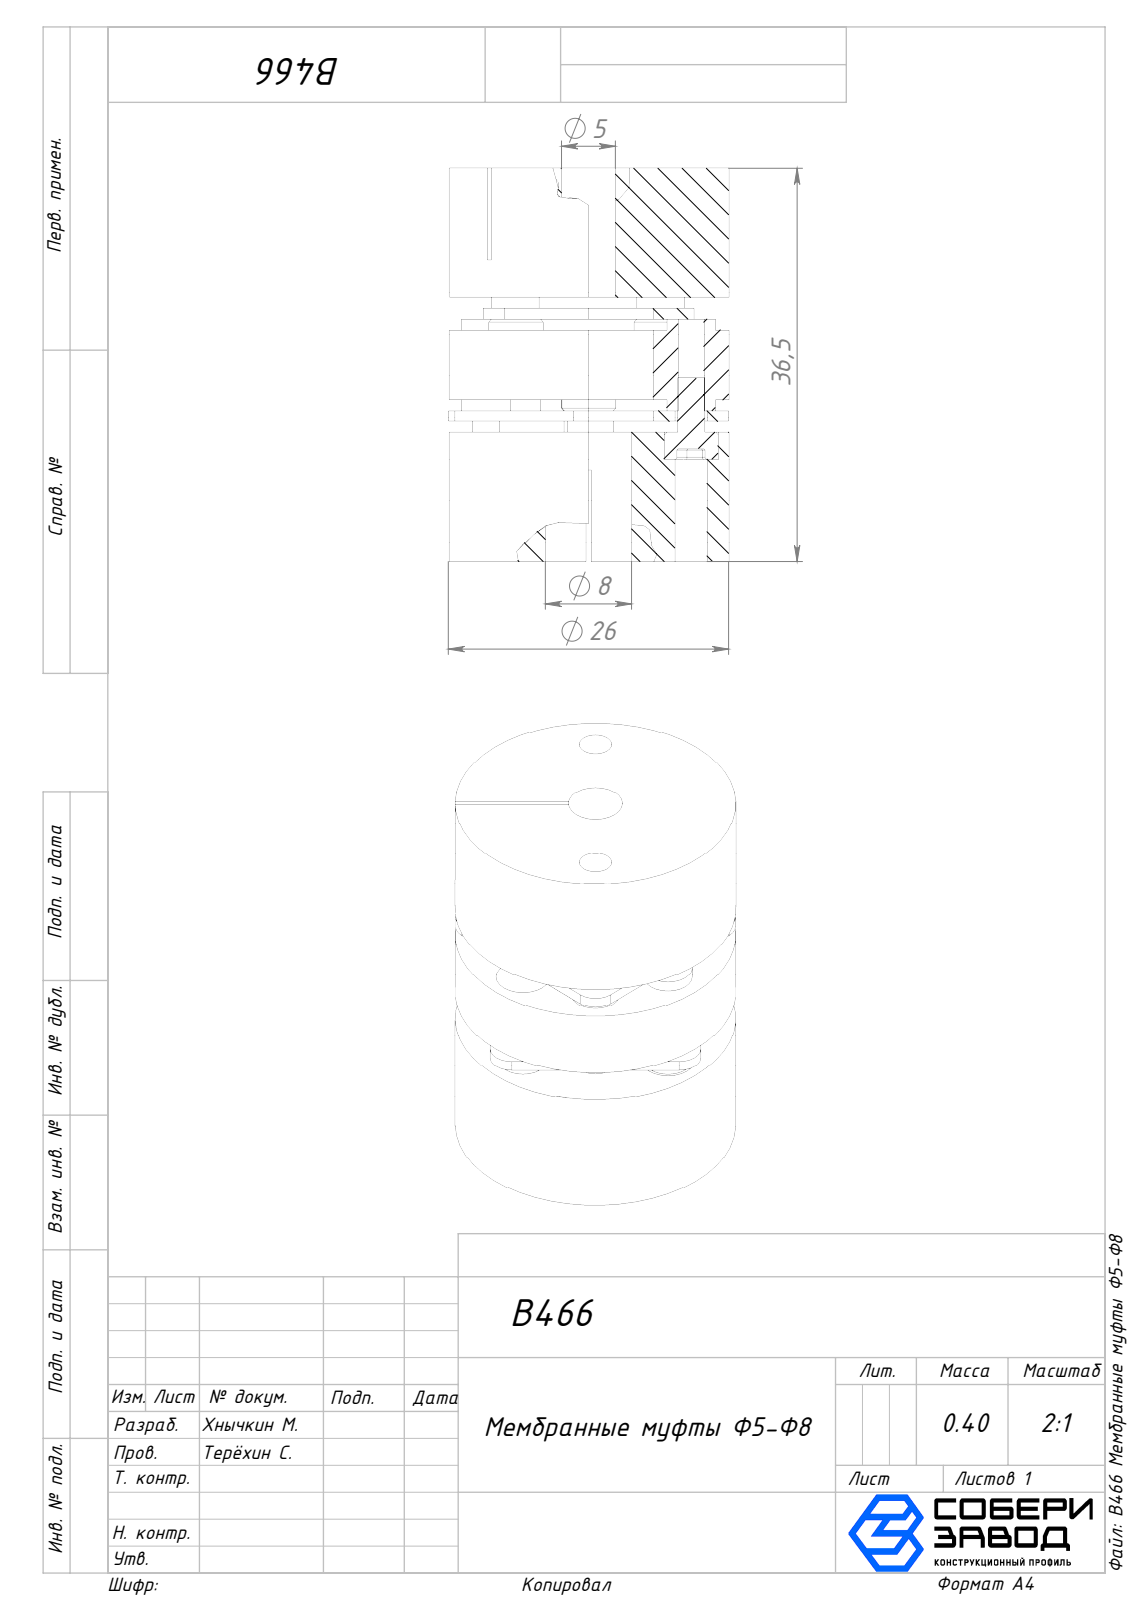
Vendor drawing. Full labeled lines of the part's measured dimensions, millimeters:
Part name (STEP PRODUCT): Средняя часть_00; Верх_00; Винт_00; Ниж.часть_00 (+1 more)
STEP written by: SolidWorks 2025 (AUTOMOTIVE_DESIGN)
Units: millimetres
Bodies: 11 solids, 362 faces (120 planar, 226 cylindrical, 16 other)
Overall size (bounding box): 36.5 × 26 × 26
Volume: 14 511 mm³ · Surface area: 9 746 mm²
Round holes (diameter × count): ⌀5 ×9, ⌀3 ×8, ⌀2.4 ×4, ⌀8 ×1, ⌀12 ×1
Round bosses / shafts (diameter × count): ⌀4.5 ×8, ⌀2.5 ×8, ⌀26 ×1
Partial cylindrical surfaces — rounded edges, fillets, slot ends (radius × count): R0.1 ×48, R0.25 ×48, R2 ×8
Main face-to-face distances: 1, 9.5, 2, 12, 10.5, 24.5, 14, 8.5, 15, 3
Hole centre spacings: 7.27, 9.5, 13.44, 17.56, 19, 19.01
